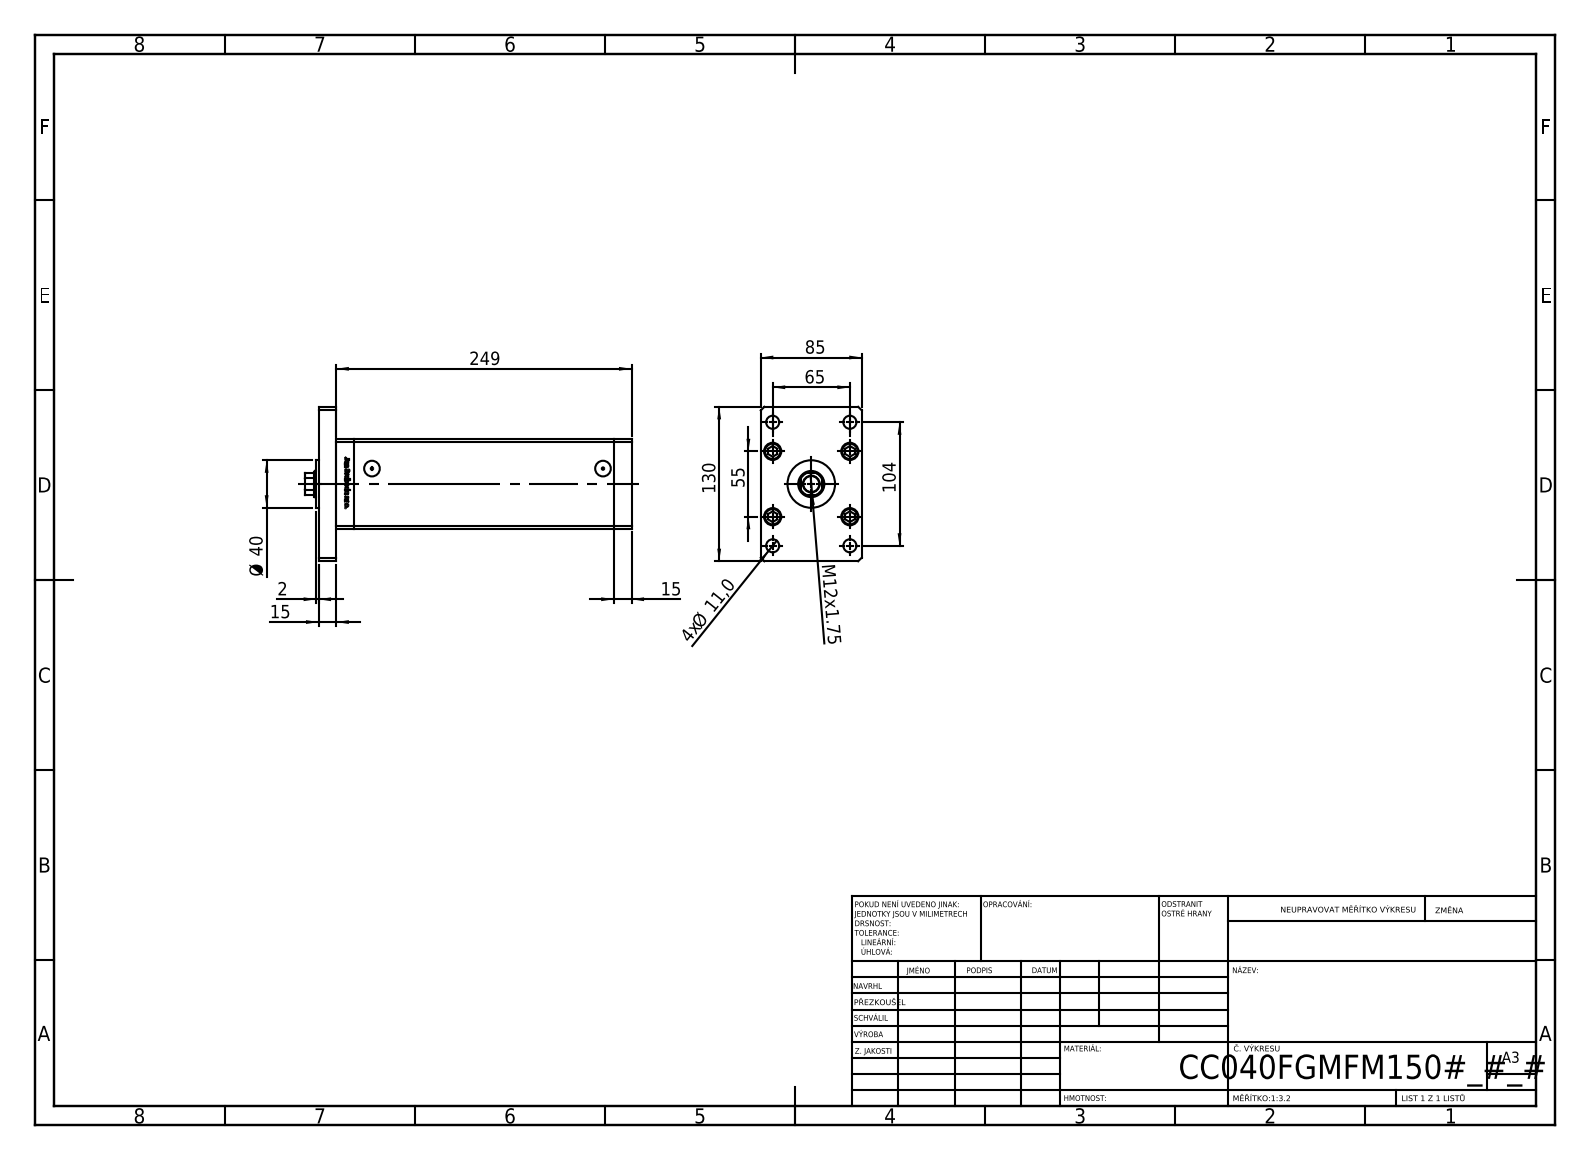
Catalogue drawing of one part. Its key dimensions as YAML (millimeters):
part_name: "V220C_VC_F; V220C BACK_F; V220C_F; V220C_F_MIDDLE (+2 more)"
step_written_by: "SolidWorks 2019 (CONFIG_CONTROL_DESIGN)"
units: millimeters
bodies: {solids: 19, faces: 1308, planar: 515, cylindrical: 187, other: 606}
overall_size: [275, 130, 85]
volume: 1536000
surface_area: 236256
round_holes:
  - {diameter: 11, count: 9}
  - {diameter: 15.5, count: 5}
  - {diameter: 10, count: 4}
  - {diameter: 14.5, count: 4}
  - {diameter: 2, count: 2}
  - {diameter: 13.16, count: 2}
  - {diameter: 13.5, count: 1}
  - {diameter: 22, count: 1}
  - {diameter: 23.5, count: 1}
round_bosses_or_shafts:
  - {diameter: 8, count: 9}
  - {diameter: 14.5, count: 5}
  - {diameter: 40, count: 1}
partial_cylinders:
  - {radius: 0.93, count: 2}
  - {radius: 10.5, count: 1}
face_to_face_distances: [15, 85, 75, 233.5, 248.5, 218.5, 30, 263.5, 10.5, 27.5]
hole_center_spacings: [28, 24.5, 42.57, 61.32, 65, 69.46, 79.5, 102.69]
